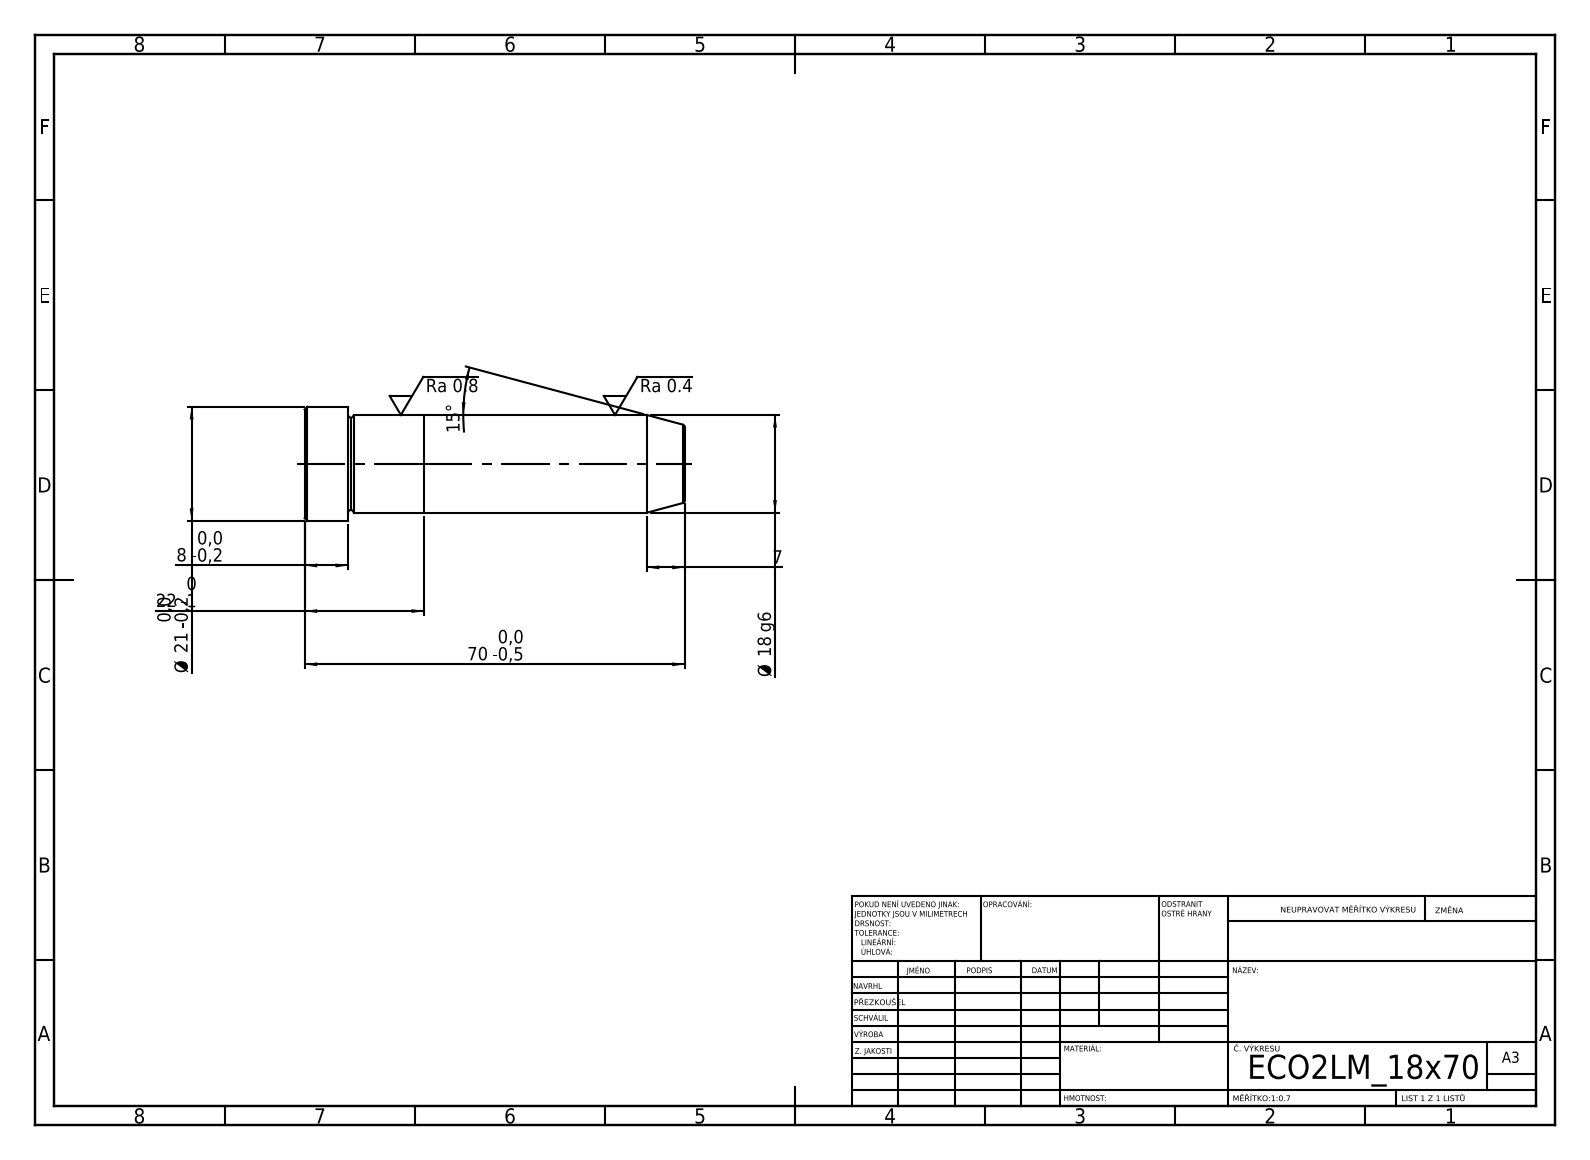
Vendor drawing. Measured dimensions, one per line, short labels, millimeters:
written by: SolidWorks 2019 (CONFIG_CONTROL_DESIGN)
unit: mm
bodies: 2 solids, 21 faces (5 planar, 6 cylindrical, 10 other)
size: 70 × 21 × 21
volume: 18 171 mm³; area: 5 116 mm²
bosses: 1× ⌀21, 1× ⌀18
face distances: 22, 48, 70, 62, 14, 8
